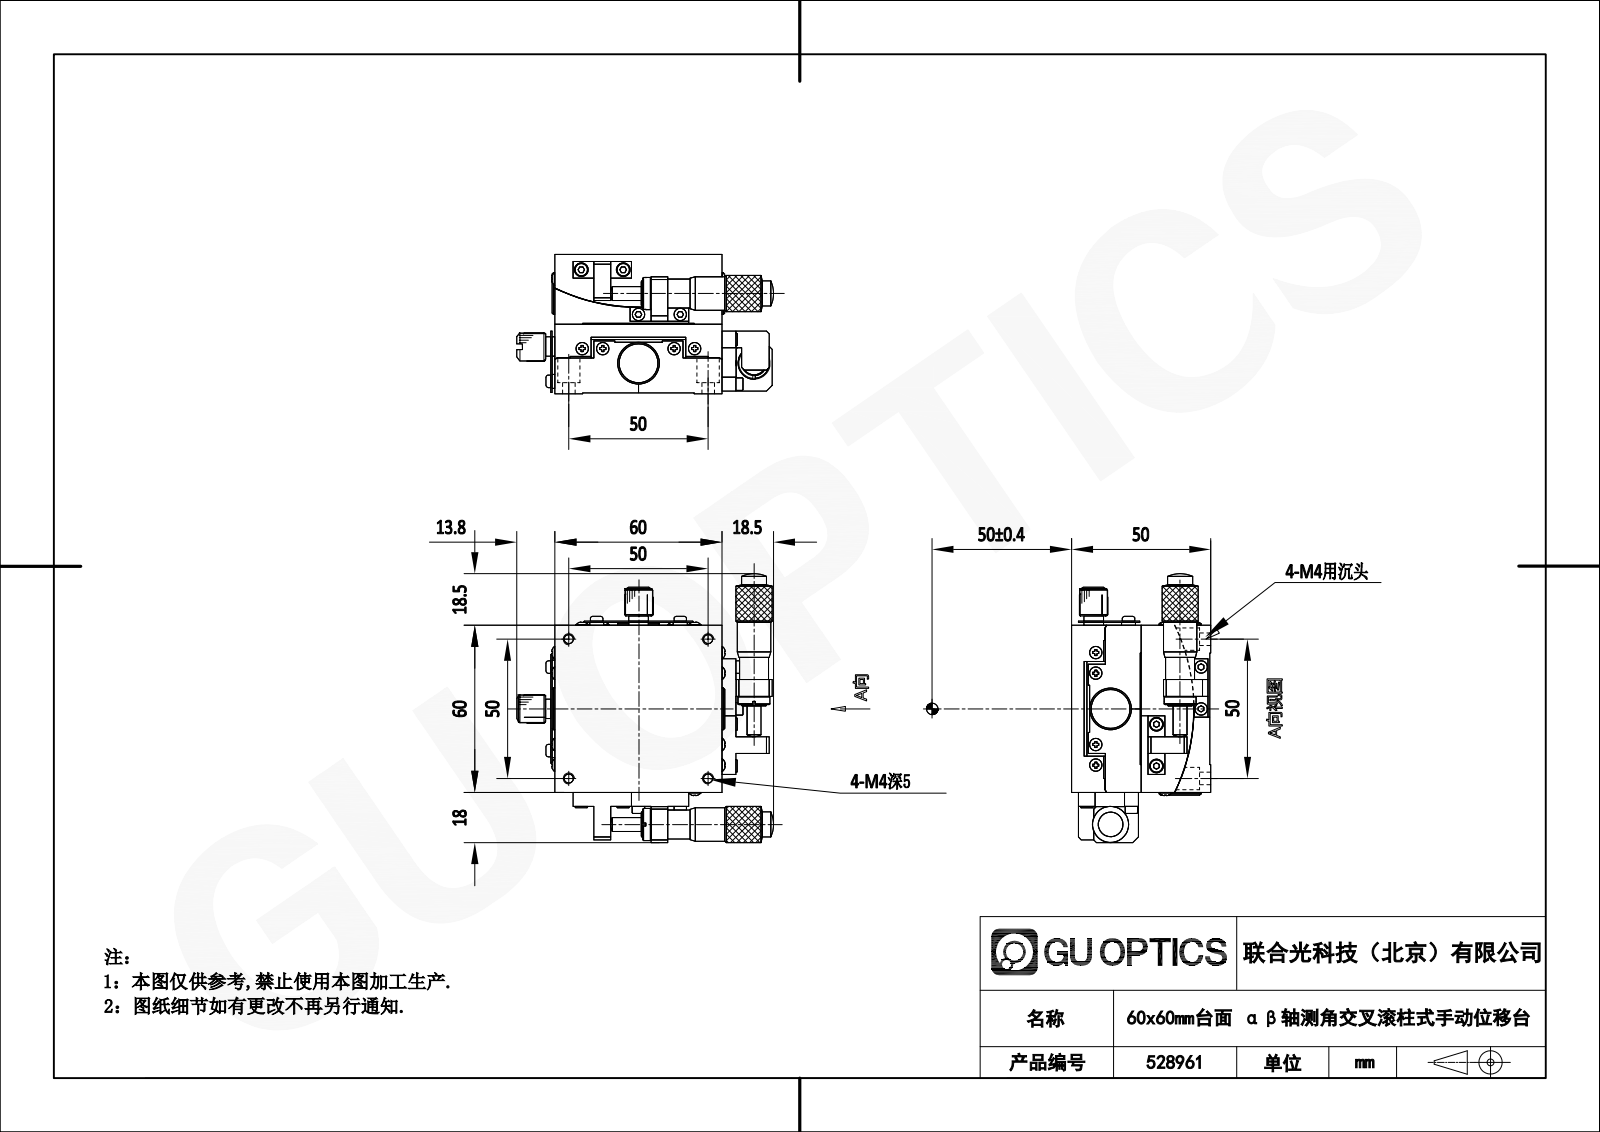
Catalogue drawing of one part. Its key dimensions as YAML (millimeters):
part_name: "528961"
step_written_by: "SolidWorks 2020 (CONFIG_CONTROL_DESIGN)"
units: millimeters
bodies: {solids: 8, faces: 4860, planar: 700, cylindrical: 1022, other: 3138}
overall_size: [112.01, 103.83, 50]
volume: 161820
surface_area: 68925
round_holes:
  - {diameter: 3.24, count: 4}
  - {diameter: 4.5, count: 4}
  - {diameter: 4.96, count: 4}
  - {diameter: 8, count: 4}
  - {diameter: 5, count: 2}
  - {diameter: 9, count: 2}
  - {diameter: 10.4, count: 2}
  - {diameter: 12, count: 2}
  - {diameter: 12.03, count: 2}
  - {diameter: 13.03, count: 2}
round_bosses_or_shafts:
  - {diameter: 4.5, count: 20}
  - {diameter: 5, count: 4}
  - {diameter: 15, count: 2}
  - {diameter: 12, count: 2}
  - {diameter: 10, count: 2}
  - {diameter: 7, count: 2}
  - {diameter: 3, count: 2}
partial_cylinders:
  - {radius: 0.45, count: 32}
  - {radius: 2, count: 16}
  - {radius: 0.63, count: 4}
  - {radius: 1.75, count: 4}
  - {radius: 3, count: 4}
  - {radius: 56.25, count: 2}
  - {radius: 59.75, count: 2}
  - {radius: 62.5, count: 2}
face_to_face_distances: [25, 24.7, 60, 5.5, 1, 19.2, 47, 14, 49.7, 13]
hole_center_spacings: [50, 15, 41.5, 70.71, 17.39, 26.32, 26.71, 33.95]
